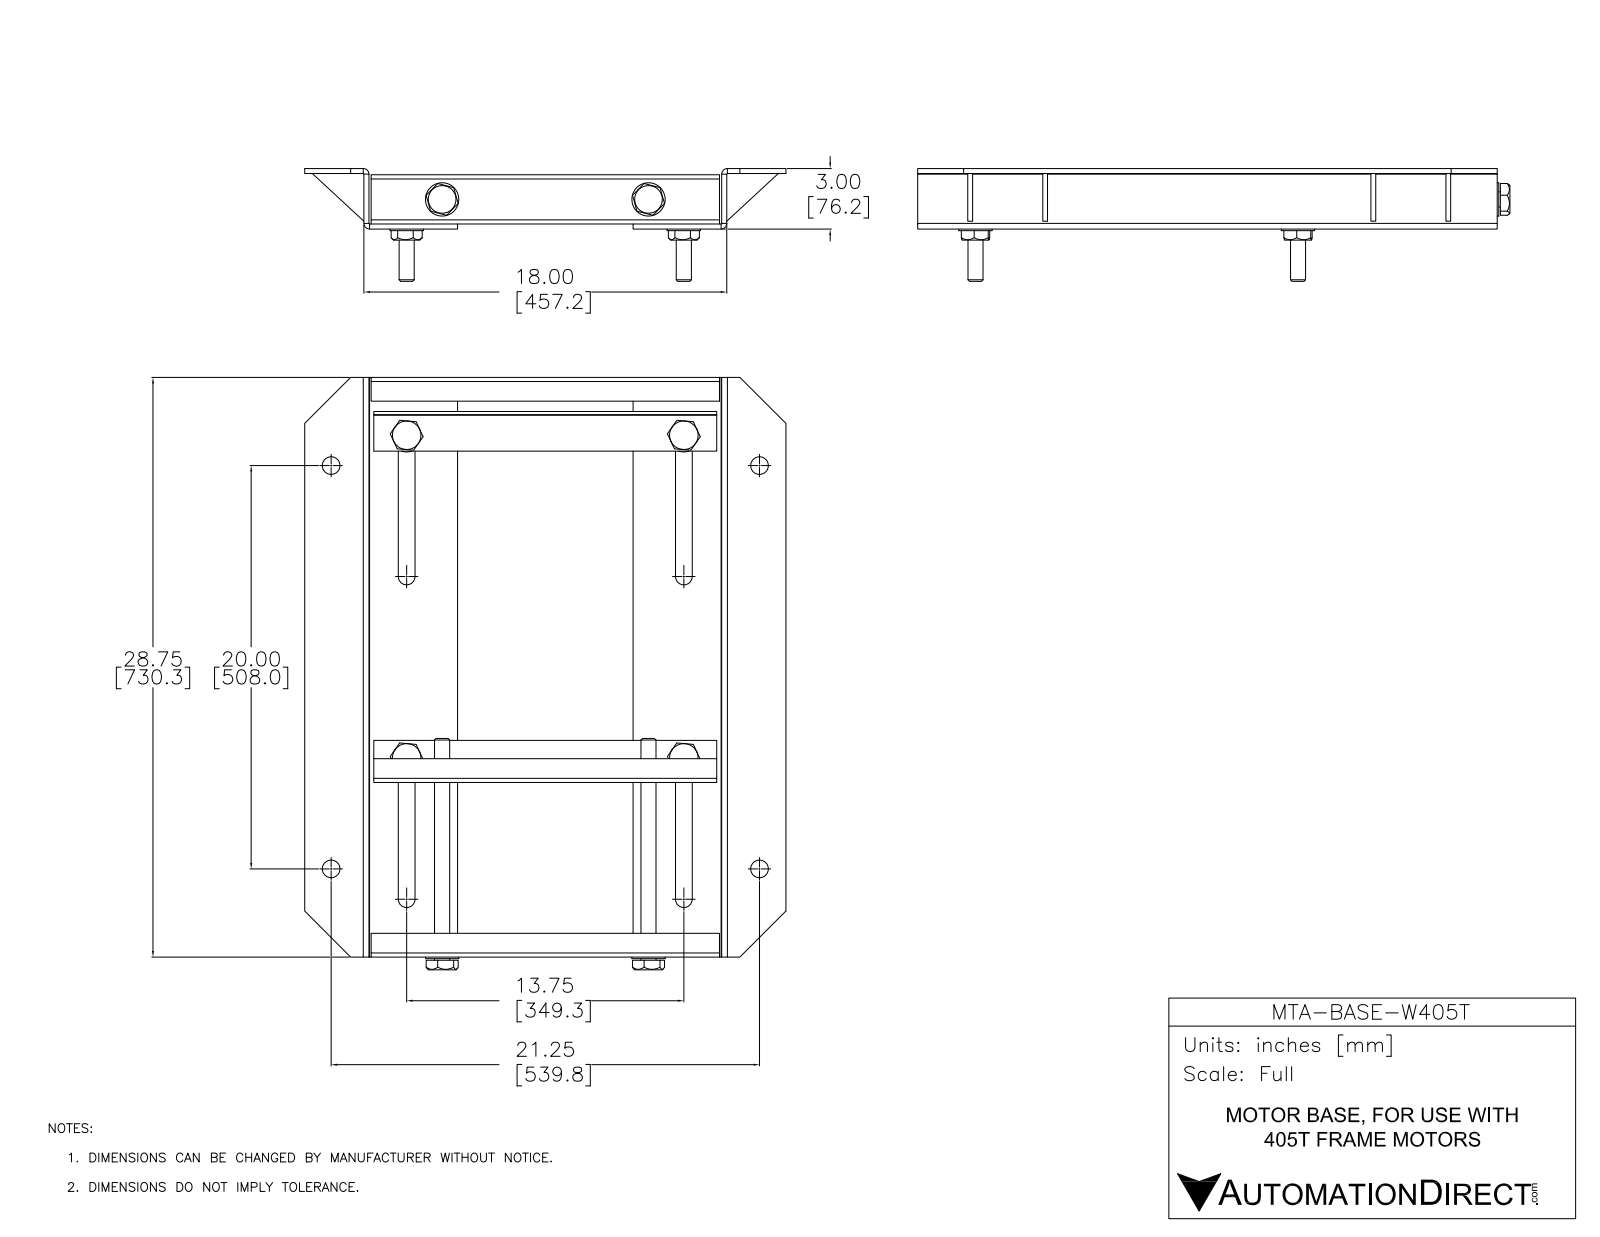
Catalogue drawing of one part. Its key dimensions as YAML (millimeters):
part_name: "W405T"
step_written_by: "SolidWorks 2017 (AUTOMOTIVE_DESIGN)"
units: millimeters
bodies: {solids: 34, faces: 426, planar: 240, cylindrical: 110, other: 76}
overall_size: [746.3, 606.4, 142.1]
volume: 3605000
surface_area: 1318000
round_holes:
  - {diameter: 19.1, count: 6}
  - {diameter: 20, count: 6}
  - {diameter: 19.1, count: 4}
  - {diameter: 22, count: 4}
  - {diameter: 22.2, count: 4}
round_bosses_or_shafts:
  - {diameter: 42, count: 6}
partial_cylinders:
  - {radius: 0.7, count: 11}
  - {radius: 10.5, count: 8}
  - {radius: 5.2, count: 6}
  - {radius: 7.1, count: 4}
  - {radius: 4.7, count: 1}
face_to_face_distances: [6.4, 69.9, 4.5, 63.5, 76.2, 450.9, 57.5, 6, 4, 457.2]
hole_center_spacings: [260, 349.3, 406.4, 508, 535.8, 539.8, 741.2, 102.5]
